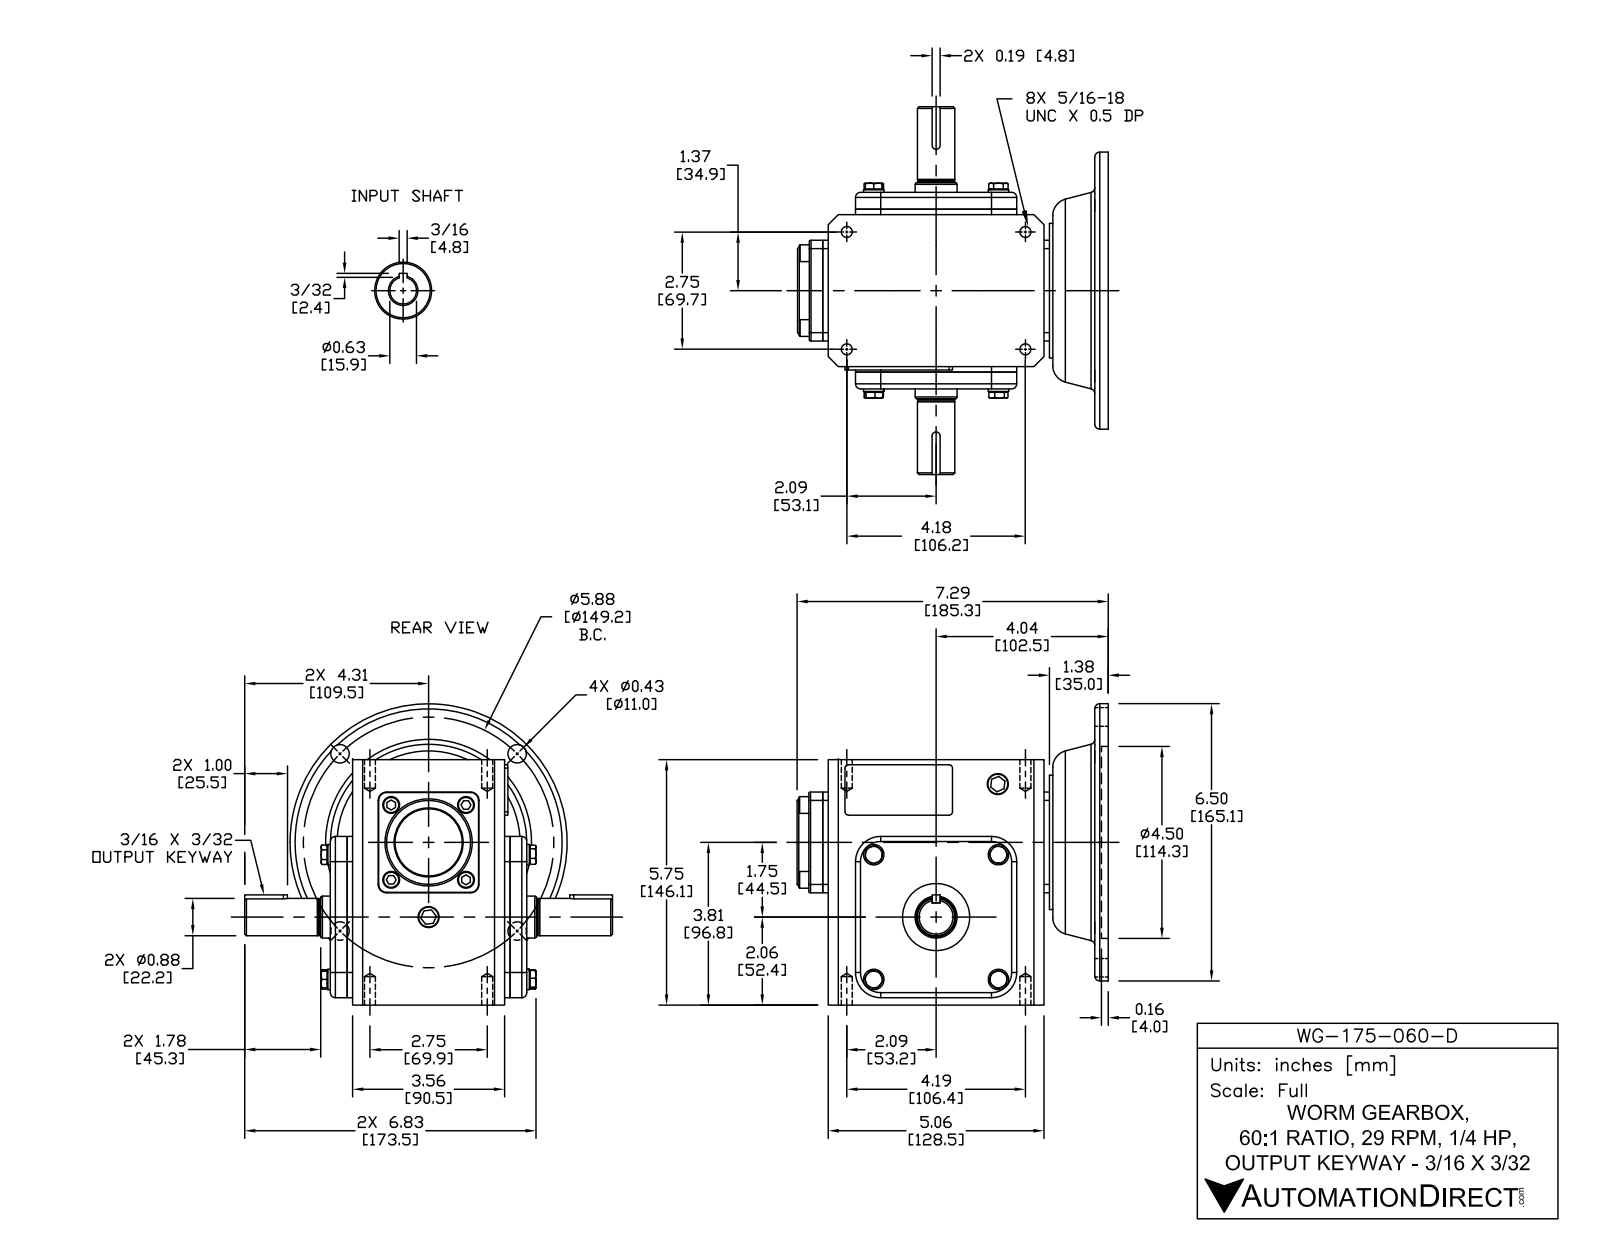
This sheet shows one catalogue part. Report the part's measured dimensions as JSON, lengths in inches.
{"part_name": "WG-175-060-D", "step_written_by": "SolidWorks 2015 (CONFIG_CONTROL_DESIGN)", "units": "inches", "bodies": {"solids": 45, "faces": 647, "planar": 324, "cylindrical": 186, "other": 137}, "overall_size": [8.622, 7.283, 7.06], "volume_in3": 133.1, "surface_area_in2": 375.6, "round_holes": [[0.257, 4], [0.406, 4], [0.512, 1], [0.625, 1], [0.984, 1], [1.181, 1], [1.457, 1], [1.575, 1], [3.543, 1], [4.5, 1]], "round_bosses_or_shafts": [[0.394, 8], [0.48, 4], [0.512, 2], [6.496, 1], [3.15, 1], [2.047, 1], [1.575, 1], [0.875, 1]], "partial_cylinders_radius": [[0.079, 8], [0.118, 8], [0.197, 4], [0.591, 4], [0.02, 2], [0.039, 2], [0.094, 2]], "face_to_face_distances": [0.128, 3.819, 4.213, 0.394, 4.085, 3.691, 0.522, 0.315, 5.75, 6.693], "hole_center_spacings": [2.937, 4.154, 2.103, 2.75, 4.188, 4.354, 5.01, 5.875]}
